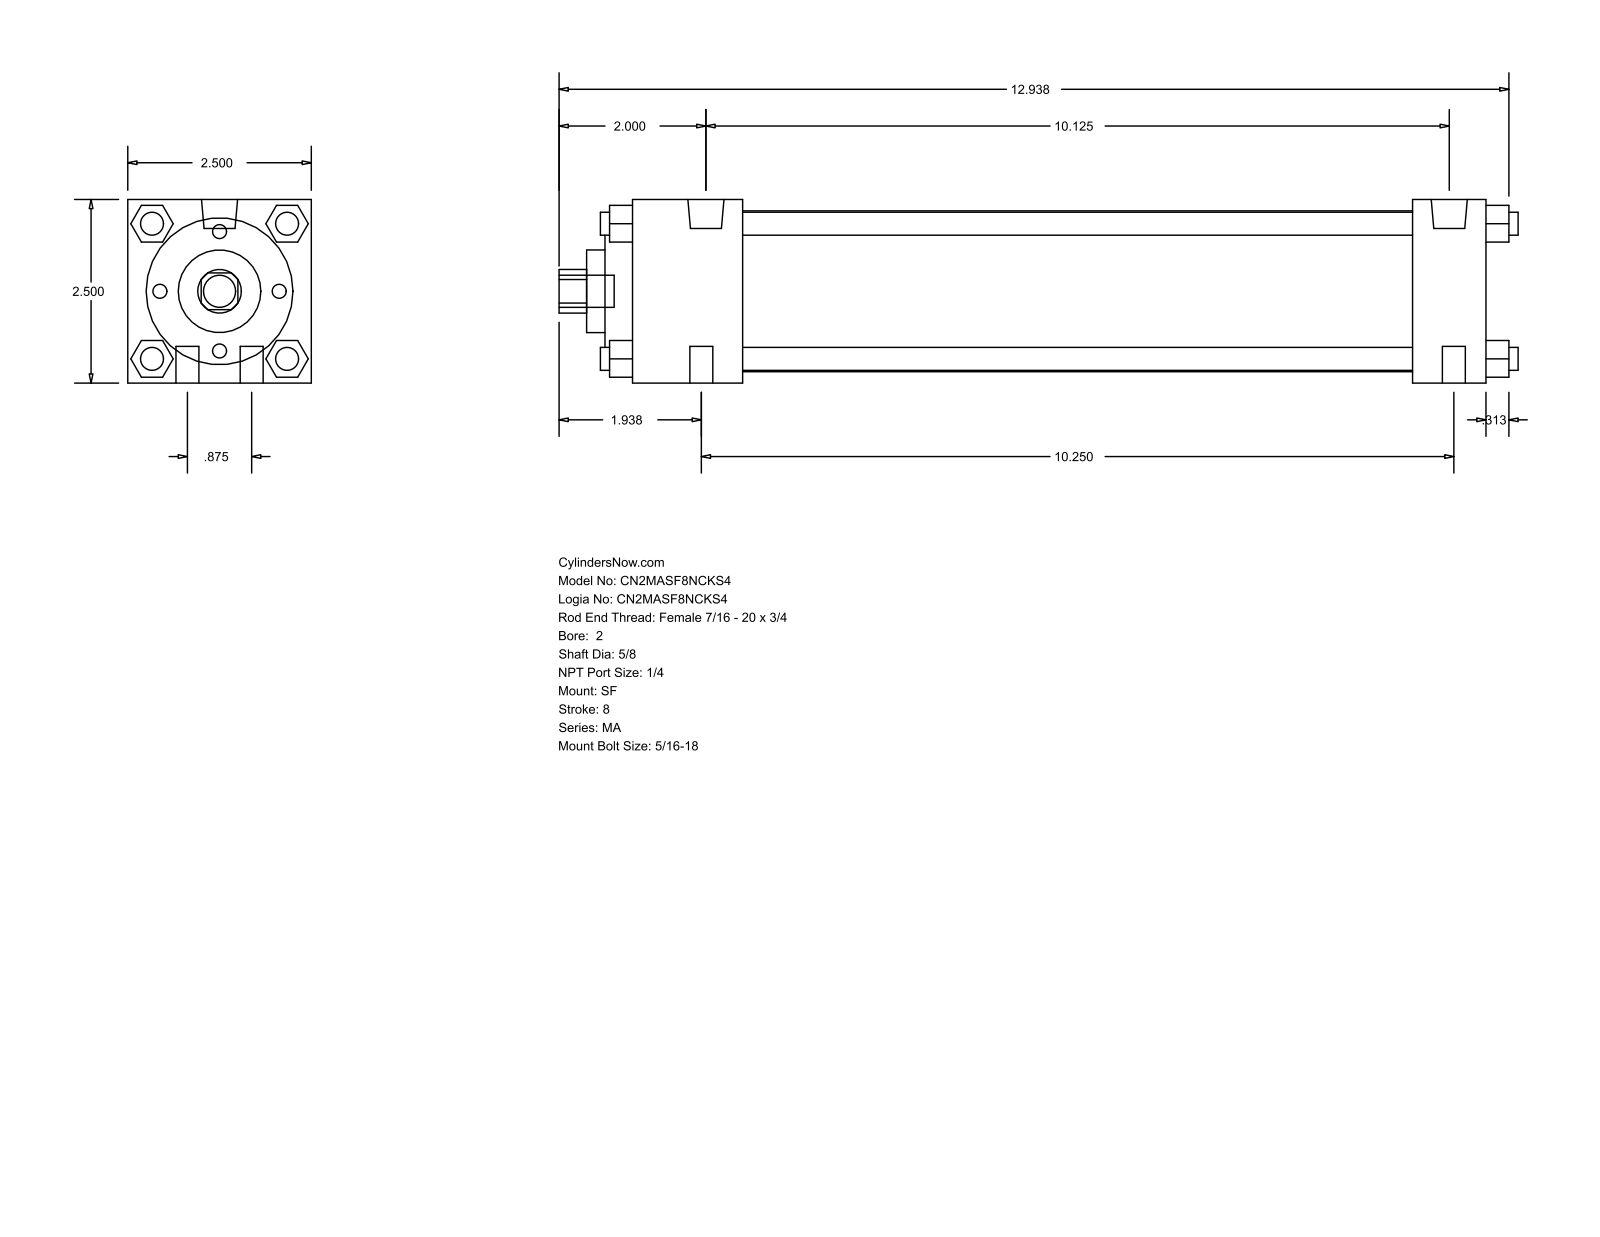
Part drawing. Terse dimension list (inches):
name: MA_SF__0200_0.625
written by: GSSL Pune (CONFIG_CONTROL_DESIGN)
unit: in
bodies: 0 solids, 126 faces (95 planar, 31 cylindrical, 0 other)
size: 13.063 × 2.5 × 2.5
holes: 1× ⌀0.625, 1× ⌀1.125, 1× ⌀2, 1× ⌀2.19
bosses: 10× ⌀0.313, 2× ⌀0.492, 1× ⌀0.437
rounds: 1× R0.297
face distances: 2.5, 0.5, 1.5, 0.375, 11.625, 10.625, 1, 9.125, 10.125, 1.875
